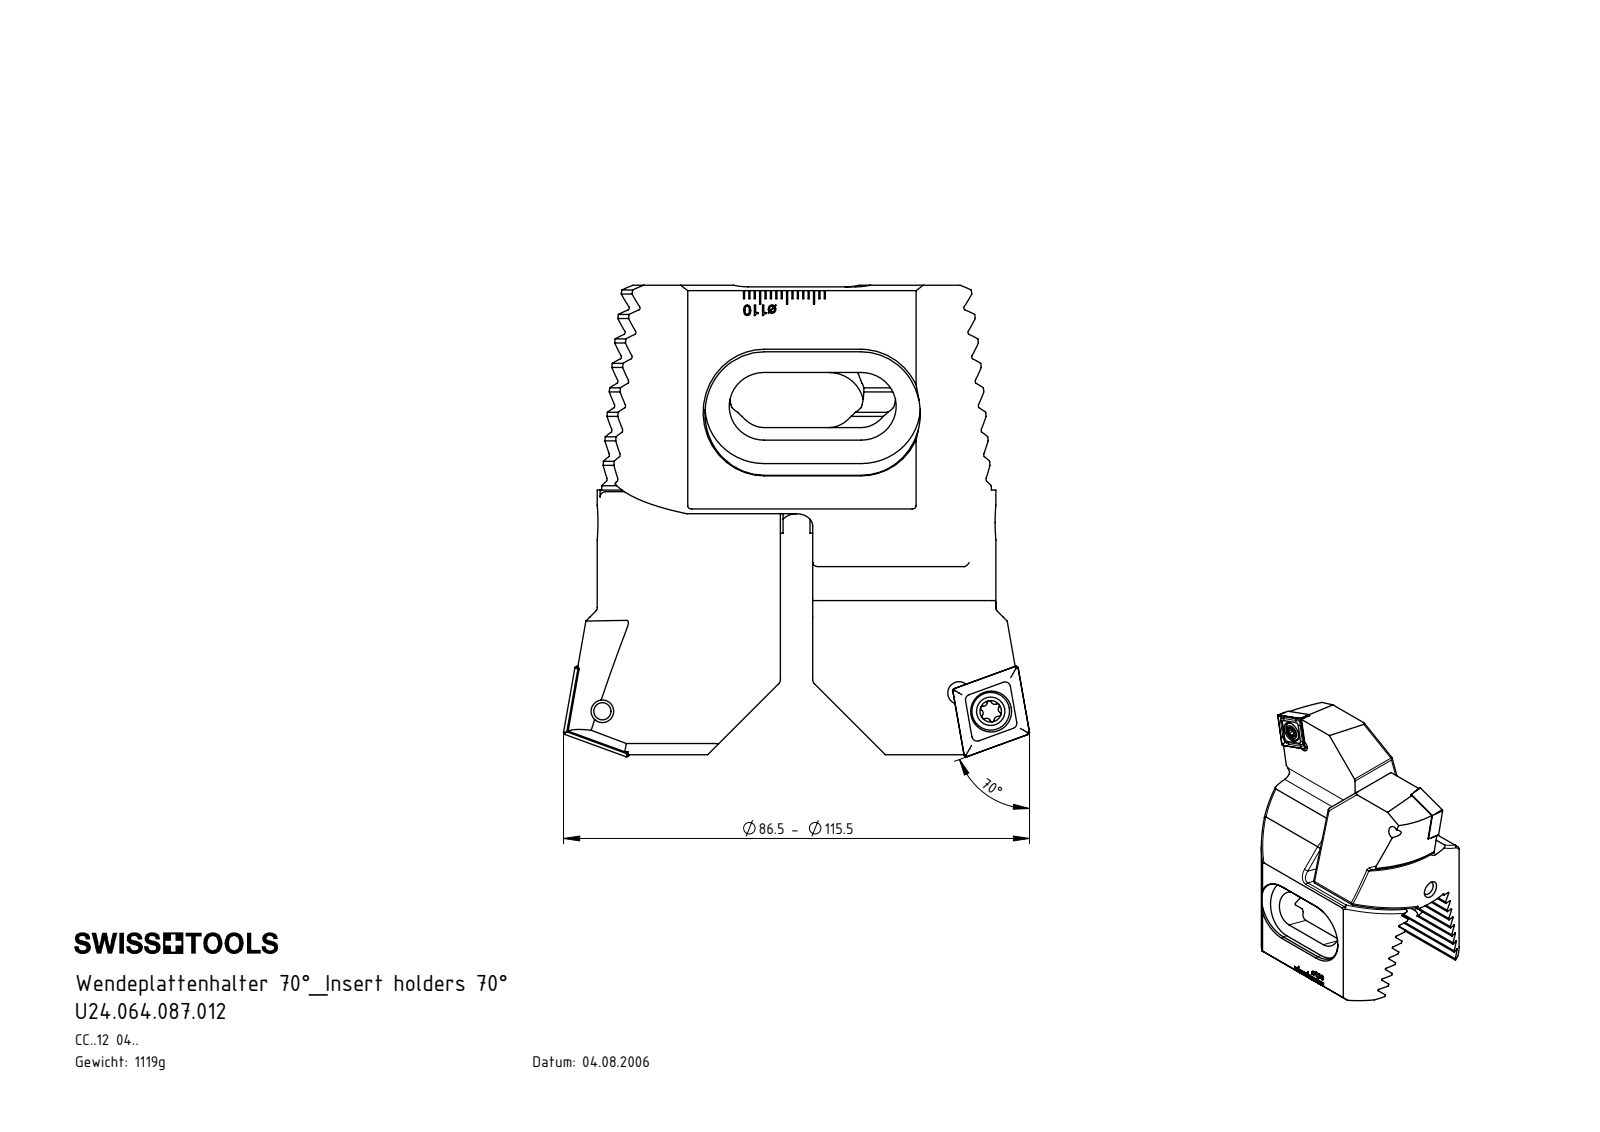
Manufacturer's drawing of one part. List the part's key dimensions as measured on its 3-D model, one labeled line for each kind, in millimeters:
Part name (STEP PRODUCT): WCC-ER2.001.010_A; CCMT120404; Z72-ER3.001.030; Z72-xxx.001.050_C_CC 12_70ø (+1 more)
STEP written by: SolidWorks 2017 (AUTOMOTIVE_DESIGN)
Units: millimetres
Bodies: 8 solids, 662 faces (398 planar, 106 cylindrical, 158 other)
Overall size (bounding box): 87.5 × 86.5 × 58.2
Volume: 143 895 mm³ · Surface area: 37 756 mm²
Round holes (diameter × count): ⌀4.2 ×4, ⌀2 ×2, ⌀5.5 ×2, ⌀7.6 ×2, ⌀5 ×1
Round bosses / shafts (diameter × count): ⌀7 ×2, ⌀5 ×2, ⌀6 ×1, ⌀4 ×1
Partial cylindrical surfaces — rounded edges, fillets, slot ends (radius × count): R0.34 ×16, R1 ×16, R0.39 ×12, R0.69 ×6, R0.69 ×6, R3 ×6, R6.5 ×4, R11 ×4
Main face-to-face distances: 4.07, 8.14, 28.8, 29.4, 20.36, 12.21, 58.2, 16.29, 20.34, 24.43
Hole centre spacings: 6.79, 6.88, 20, 66.29, 66.37, 72.16, 38.64, 60.32
